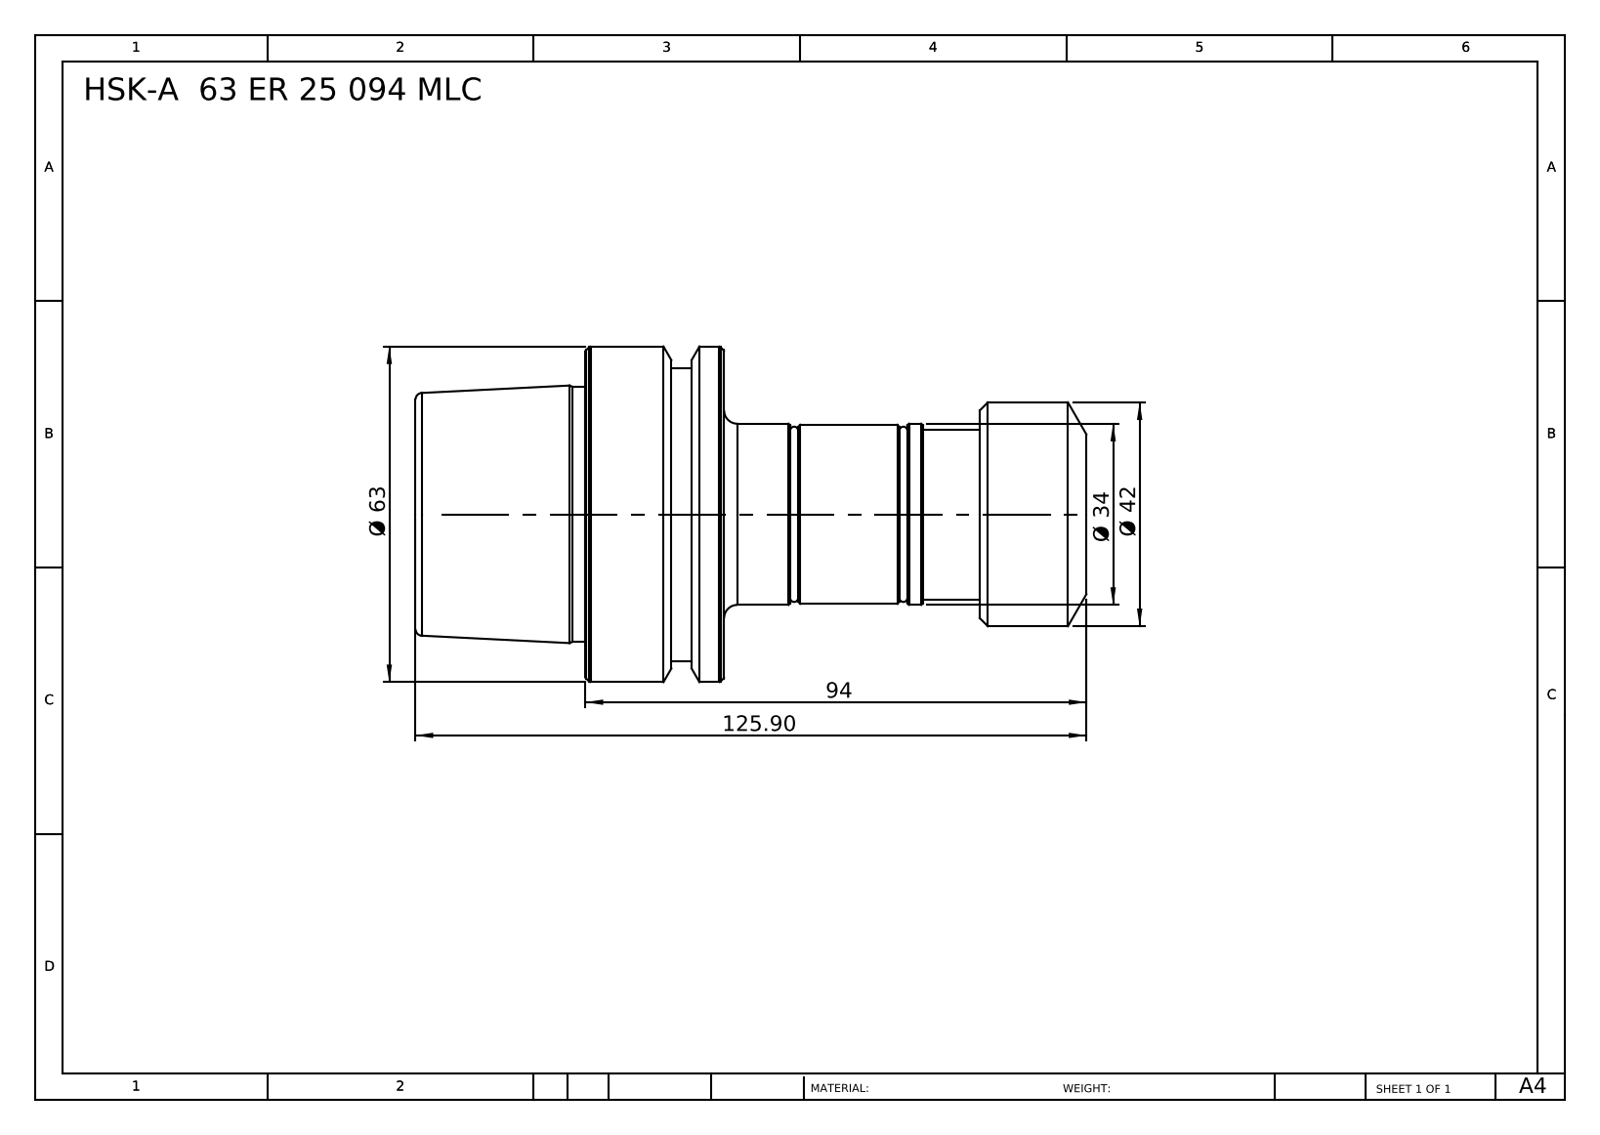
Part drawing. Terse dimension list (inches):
name: HSK-A 63 ER 25 094 MLC
written by: SolidWorks 2014 (CONFIG_CONTROL_DESIGN)
unit: in
bodies: 1 solid, 76 faces (12 planar, 18 cylindrical, 46 other)
size: 4.957 × 2.48 × 2.48
volume: 12.25 in³; area: 39.45 in²
bosses: 1× ⌀2.48, 1× ⌀2.165, 1× ⌀1.881, 1× ⌀1.654, 1× ⌀1.339, 1× ⌀1.322, 1× ⌀1.256
face distances: 2.28, 1.024, 1.256, 2.677, 3.701, 4.957, 1.89, 0.787, 2.913, 4.169
